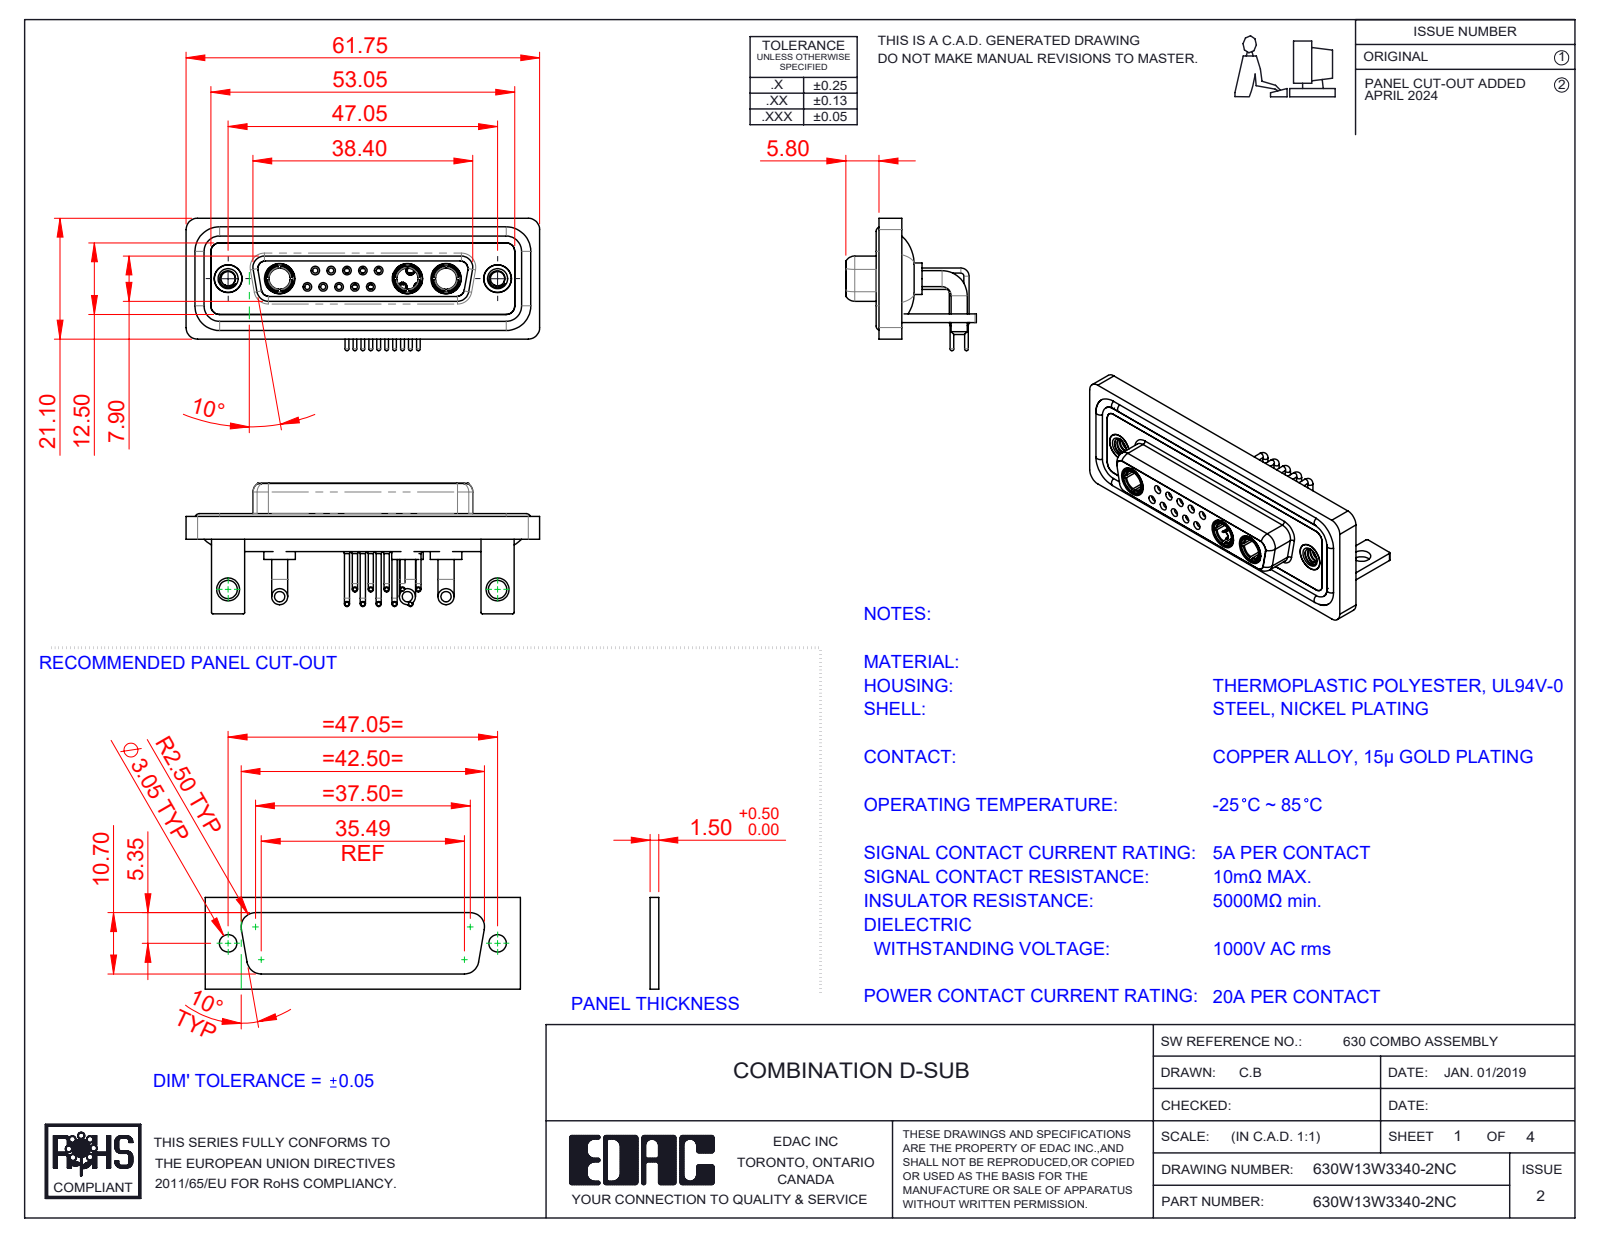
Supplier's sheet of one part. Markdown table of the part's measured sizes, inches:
| quantity | value |
| --- | --- |
| part name | 630W13W3340-2NC; 630Combo Contact Row 2_50 Contacts; 630Combo Waterproof Housing_25 Contacts; Power Socket_20A RA (+6 more) |
| STEP written by | SolidWorks 2023 (CONFIG_CONTROL_DESIGN) |
| units | inches |
| bodies | 25 solids, 1192 faces (362 planar, 515 cylindrical, 315 other) |
| overall size | 2.431 × 0.91 × 0.898 |
| volume | 0.539 in³ |
| surface area | 23.3 in² |
| round holes (diameter × count) | 0.035 × 10, 0.043 × 10, 0.059 × 10, 0.079 × 10, 0.063 × 5, 0.067 × 5, 0.191 × 5, 0.146 × 3, 0.209 × 3, 0.098 × 2, 0.126 × 2, 0.157 × 2 |
| round bosses / shafts (diameter × count) | 0.035 × 15, 0.063 × 12, 0.026 × 10, 0.11 × 6, 0.079 × 5, 0.059 × 5, 0.217 × 3, 0.205 × 3 |
| partial cylindrical surfaces (radius × count) | 0.079 × 19, 0.059 × 18, 0.01 × 16, 0.053 × 8, 0.063 × 8, 0.02 × 5, 0.024 × 4, 0.026 × 4 |
| main face-to-face distances | 0.016, 0.071, 0.114, 0.146, 0.059, 0.161, 0.043, 0.055, 0.063, 0.122 |
| hole center spacings | 0.124, 0.109, 0.218, 0.198, 0.327, 0.198, 0.295, 0.436 |
